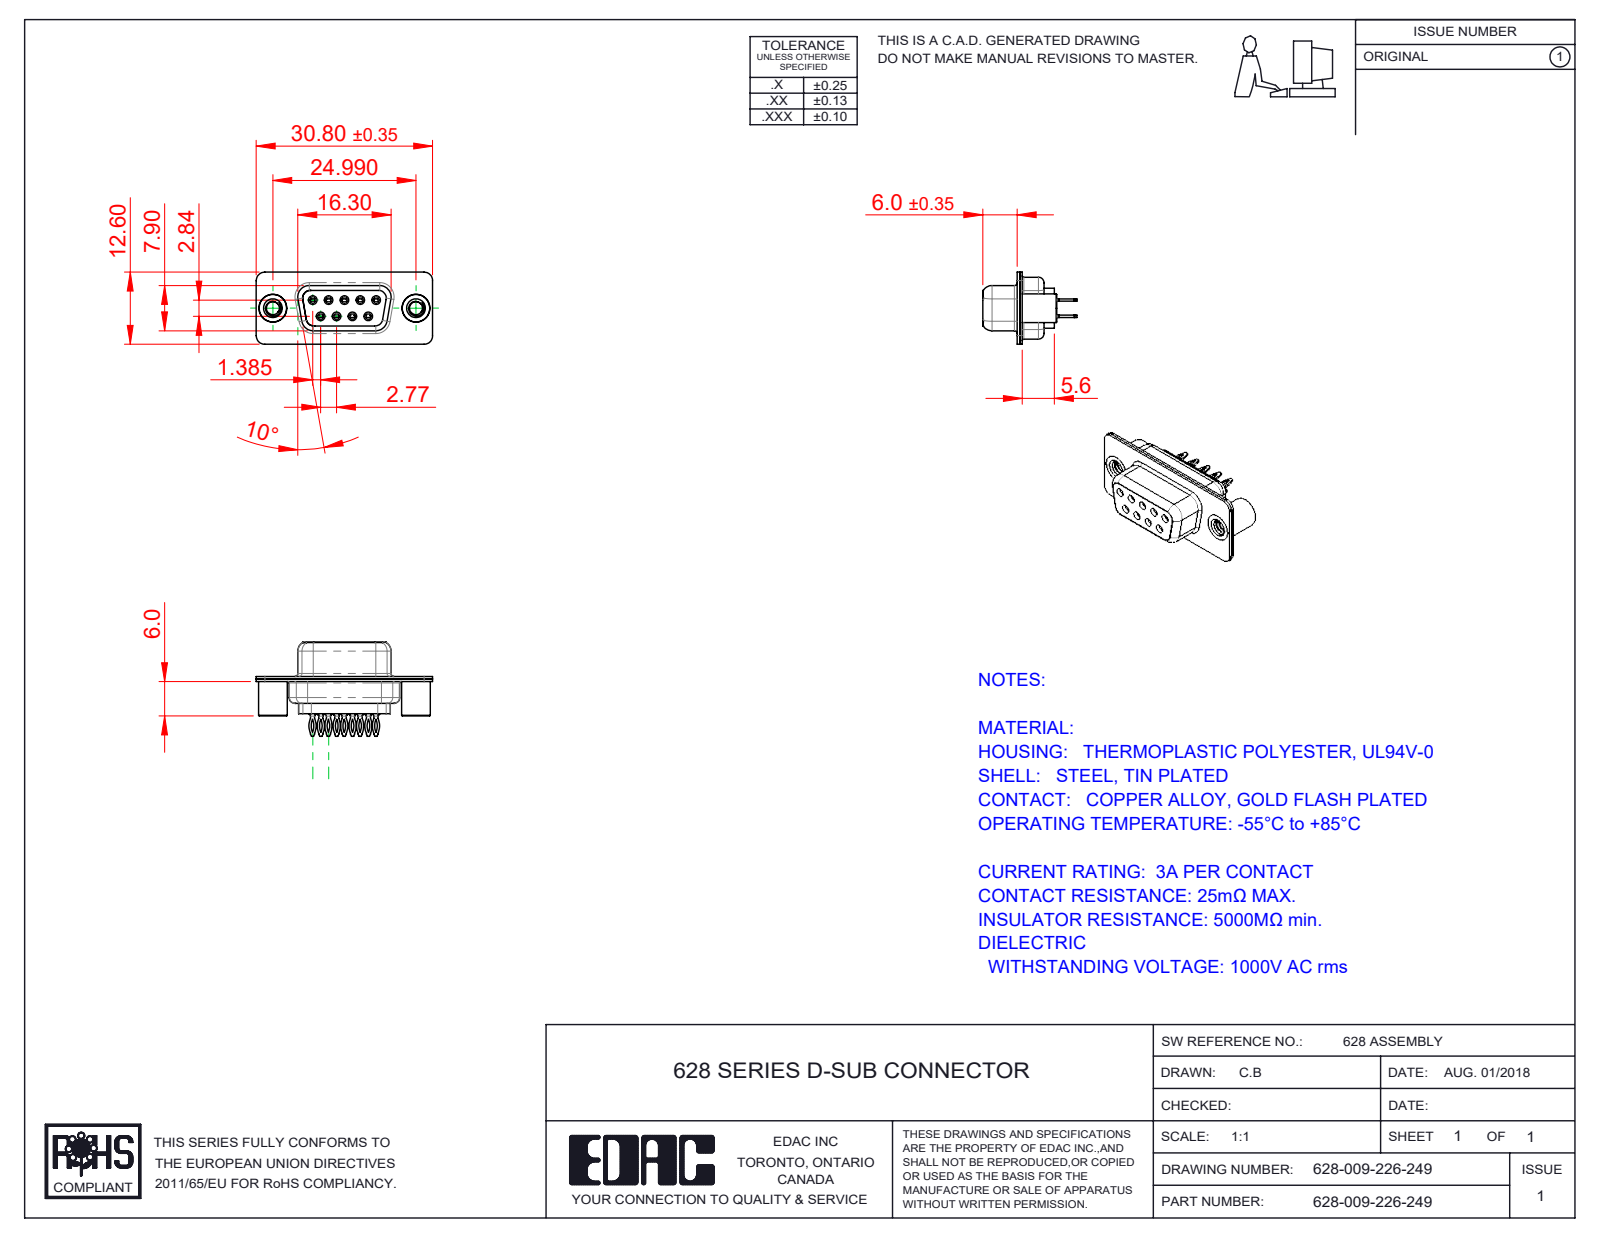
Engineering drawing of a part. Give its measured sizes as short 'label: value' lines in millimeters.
name: 628 Contact Row 2_26L; 628-009-226-249; 628 4-40 Threaded Standoff BS; 628 Housing_09 LP (+3 more)
written by: SolidWorks 2020 (CONFIG_CONTROL_DESIGN)
unit: mm
bodies: 14 solids, 1210 faces (310 planar, 400 cylindrical, 500 other)
size: 30.8 × 16.45 × 12.6
volume: 1 854 mm³; area: 4 668 mm²
holes: 9× ⌀0.8, 9× ⌀0.9, 9× ⌀1.1, 9× ⌀1.6, 5× ⌀1.7, 2× ⌀2.26, 2× ⌀4, 2× ⌀4.05, 2× ⌀4.85
bosses: 9× ⌀2, 9× ⌀1.5, 9× ⌀1.2, 2× ⌀5, 2× ⌀4.95, 2× ⌀4.8
rounds: 18× R2.92, 18× R3.33, 17× R1.5, 12× R2, 9× R0.28, 6× R1.35, 4× R0.25, 4× R0.5
face distances: 0.45, 0.4, 0.9, 1.9, 8.5, 6.6, 1.4, 6.5, 0.5, 6
hole spacings: 3.16, 2.77, 5.54, 5.03, 5.04, 8.31, 7.48, 7.49
